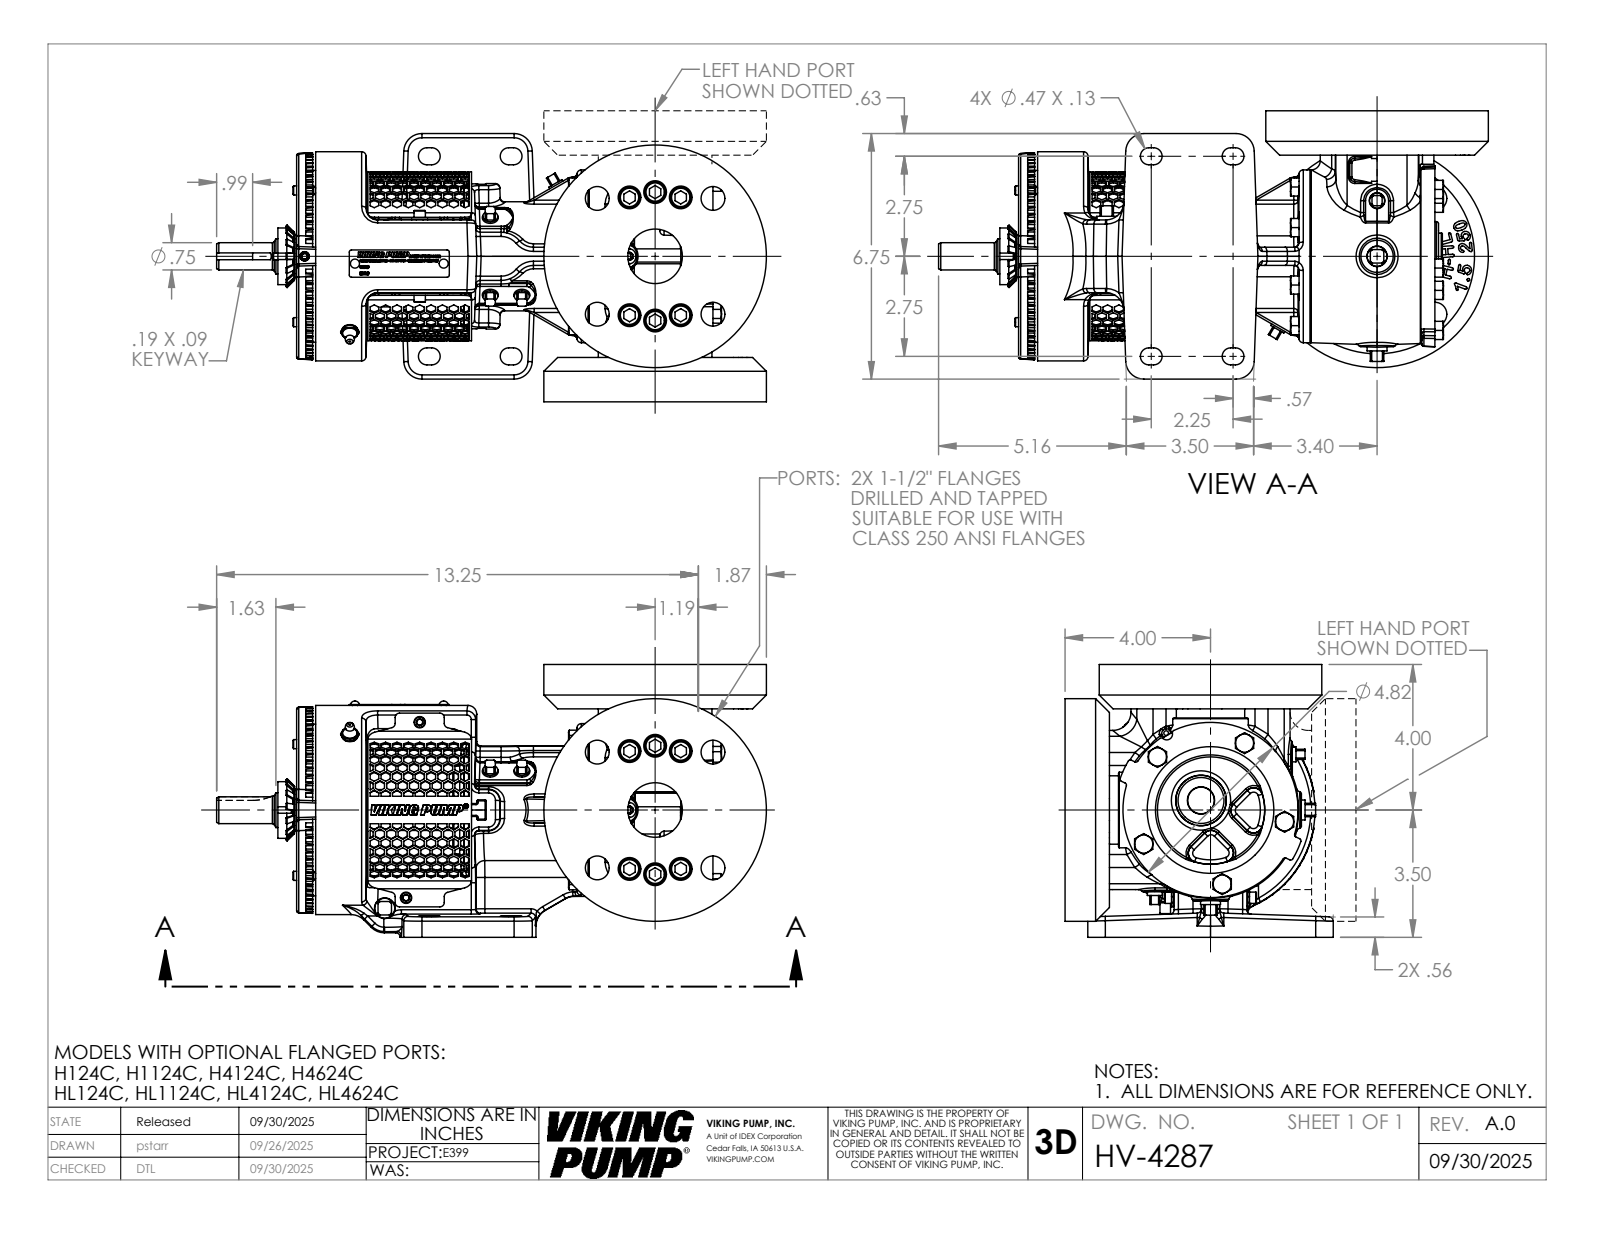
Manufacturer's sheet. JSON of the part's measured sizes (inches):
{"part_name": "HV-4287", "step_written_by": "SolidWorks 2024 (AUTOMOTIVE_DESIGN)", "units": "inches", "bodies": {"solids": 1, "faces": 4228, "planar": 1431, "cylindrical": 876, "other": 1921}, "overall_size": [15.119, 7.5, 7.375], "volume_in3": 241.8, "surface_area_in2": 653, "round_holes": [[0.25, 9], [0.625, 8], [0.656, 8], [0.625, 4], [0.159, 3], [0.198, 3], [0.257, 2], [1.5, 2], [0.989, 1], [1.265, 1], [4.502, 1]], "round_bosses_or_shafts": [[0.563, 12], [0.312, 3], [0.19, 3], [6.12, 2], [0.25, 2], [5.75, 1], [4.75, 1], [4.747, 1]], "partial_cylinders_radius": [[0.054, 140], [0.12, 103], [0.06, 49], [0.5, 34], [0.03, 22], [0.24, 11], [0.25, 10], [0.234, 8]], "face_to_face_distances": [7.5, 1.22, 1.94, 6.28, 11.449, 9.509, 0.524, 1.417, 10.925, 0.44], "hole_center_spacings": [1.766, 2.56, 0.719, 0.887, 1.6, 2.25, 2.295, 3.182]}
